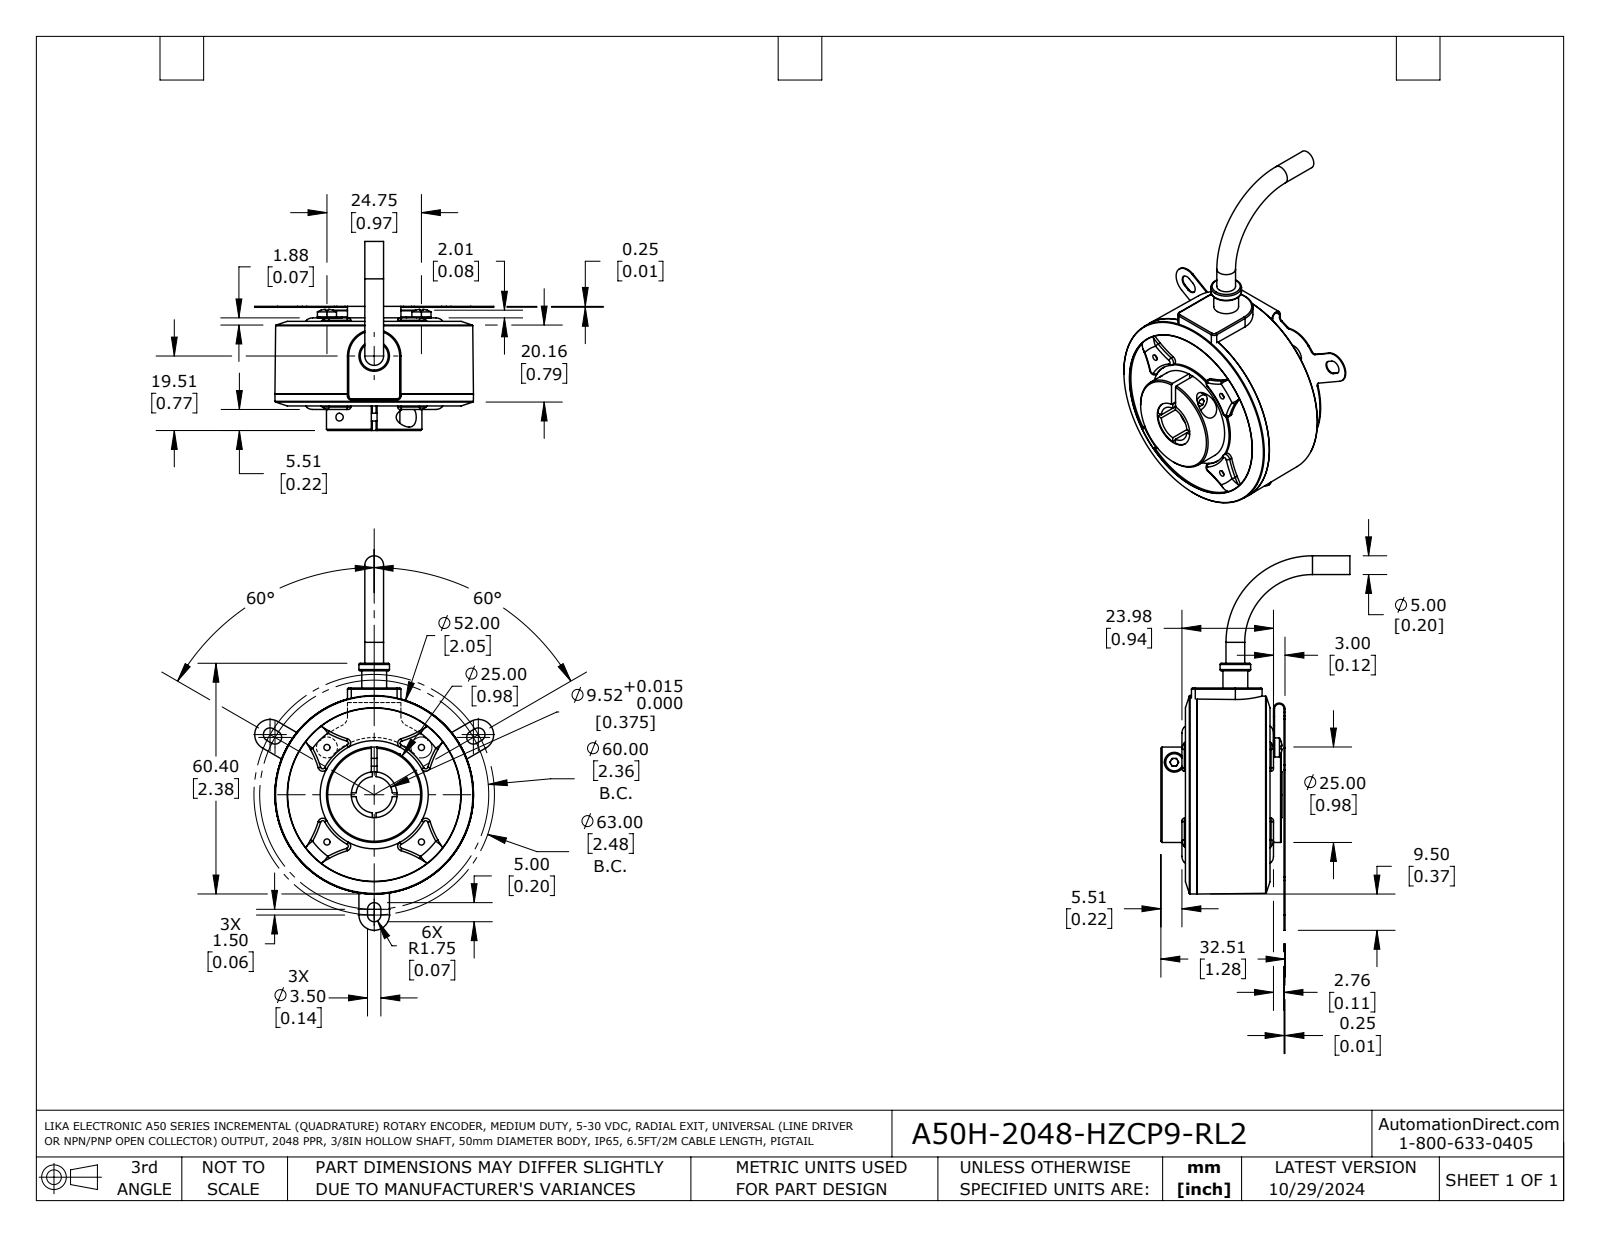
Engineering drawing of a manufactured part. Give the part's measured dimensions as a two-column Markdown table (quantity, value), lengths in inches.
| quantity | value |
| --- | --- |
| part name | A50H-2048-HZCP9-RL2 |
| STEP written by | SolidWorks 2021 (AUTOMOTIVE_DESIGN) |
| units | inches |
| bodies | 8 solids, 504 faces (168 planar, 160 cylindrical, 176 other) |
| overall size | 3.86 × 2.464 × 1.949 |
| volume | 3.657 in³ |
| surface area | 31.76 in² |
| round holes (diameter × count) | 0.064 × 4, 0.11 × 3, 0.217 × 2, 0.081 × 1, 0.205 × 1, 0.375 × 1, 0.472 × 1, 1.024 × 1, 1.115 × 1, 1.786 × 1 |
| round bosses / shafts (diameter × count) | 0.098 × 4, 0.197 × 2, 0.193 × 2, 0.984 × 1, 0.315 × 1, 0.256 × 1, 0.177 × 1 |
| partial cylindrical surfaces (radius × count) | 0.039 × 12, 0.008 × 8, 0.008 × 6, 0.069 × 6, 0.157 × 3, 0.01 × 2, 0.013 × 2, 0.098 × 2 |
| main face-to-face distances | 0.896, 0.906, 0.154, 0.144, 0.751, 1.009, 0.999, 0.854, 0.103, 0.709 |
| hole center spacings | 0.583, 0.689, 0.974, 1.383, 0.807, 1.378, 1.614 |
